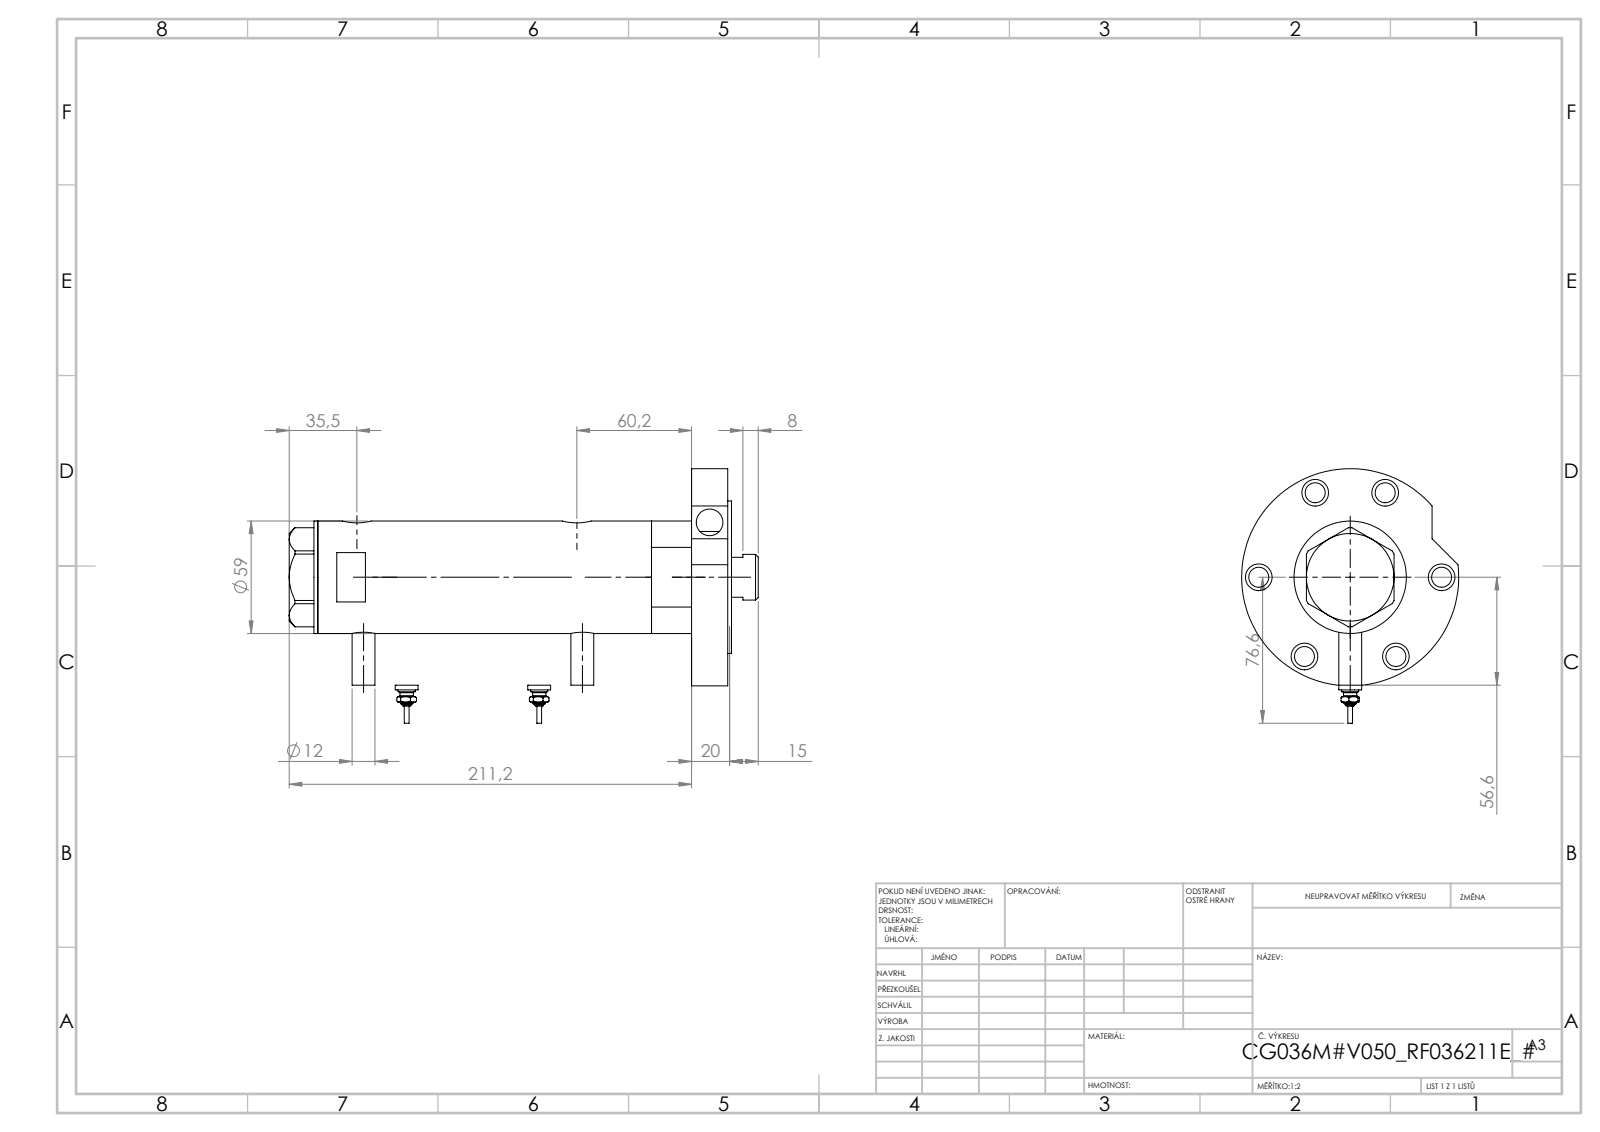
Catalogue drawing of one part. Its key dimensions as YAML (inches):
part_name: "V270CG_RF211E; V270CG_VC; V270CG_MIDDLE; V270CG_FRONT (+2 more)"
step_written_by: "SolidWorks 2019 (CONFIG_CONTROL_DESIGN)"
units: inches
bodies: {solids: 7, faces: 256, planar: 90, cylindrical: 102, other: 64}
overall_size: [9.693, 5.26, 4.488]
volume: 43.71
surface_area: 233.5
round_holes:
  - {diameter: 0.551, count: 7}
  - {diameter: 0.413, count: 6}
  - {diameter: 0.383, count: 2}
  - {diameter: 0.492, count: 2}
  - {diameter: 0.591, count: 2}
  - {diameter: 0.335, count: 1}
  - {diameter: 0.984, count: 1}
  - {diameter: 1.043, count: 1}
  - {diameter: 1.417, count: 1}
  - {diameter: 1.575, count: 1}
  - {diameter: 1.89, count: 1}
  - {diameter: 2.047, count: 1}
round_bosses_or_shafts:
  - {diameter: 0.472, count: 4}
  - {diameter: 0.354, count: 2}
  - {diameter: 0.276, count: 2}
  - {diameter: 0.177, count: 2}
  - {diameter: 0.098, count: 2}
  - {diameter: 4.488, count: 1}
  - {diameter: 3.15, count: 1}
  - {diameter: 2.323, count: 1}
face_to_face_distances: [0.079, 0.748, 0.827, 8.551, 7.724, 8.472, 5.402, 2.323, 3.071, 3.15]
hole_center_spacings: [1.89, 2.1, 3.143, 3.273, 3.39, 3.772, 0.114, 0.138]
